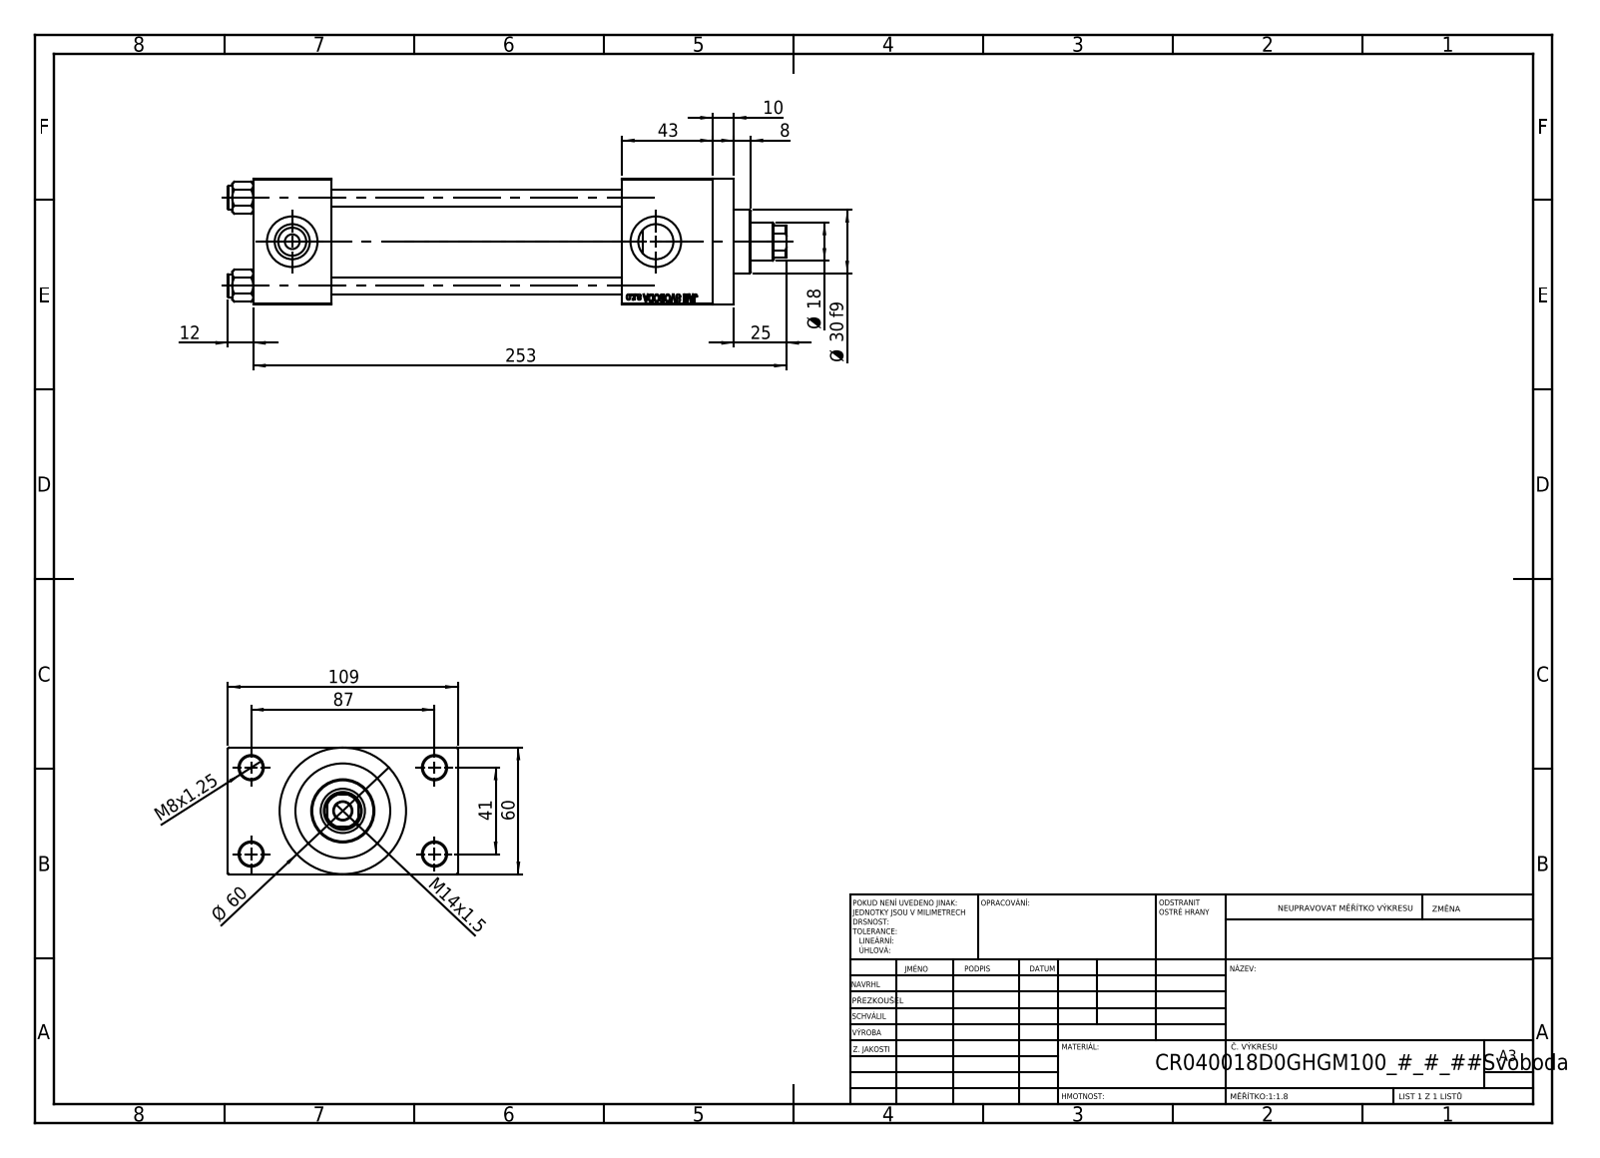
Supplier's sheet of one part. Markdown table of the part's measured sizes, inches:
| quantity | value |
| --- | --- |
| part name | V215_VC_A; V215CR_D_Body; V215CR_D_TYCINKA; NUT_M5_D (+1 more) |
| STEP written by | SolidWorks 2019 (CONFIG_CONTROL_DESIGN) |
| units | inches |
| bodies | 11 solids, 1104 faces (498 planar, 88 cylindrical, 518 other) |
| overall size | 10.433 × 4.291 × 2.362 |
| volume | 35.48 in³ |
| surface area | 242.9 in² |
| round holes (diameter × count) | 0.315 × 4, 0.433 × 4, 0.276 × 2, 0.656 × 2, 0.945 × 2, 0.335 × 1, 0.709 × 1, 0.827 × 1, 1.22 × 1, 1.575 × 1, 1.772 × 1 |
| round bosses / shafts (diameter × count) | 0.433 × 4, 2.362 × 1, 1.811 × 1, 1.181 × 1 |
| partial cylindrical surfaces (radius × count) | 0.335 × 1 |
| main face-to-face distances | 2.362, 5.433, 0.965, 3.327, 1.457, 6.89, 8.583, 7.126, 1.693, 0.394 |
| hole center spacings | 0.892, 1.161, 1.642, 1.856, 1.893, 2.533, 3.011, 1.614 |
